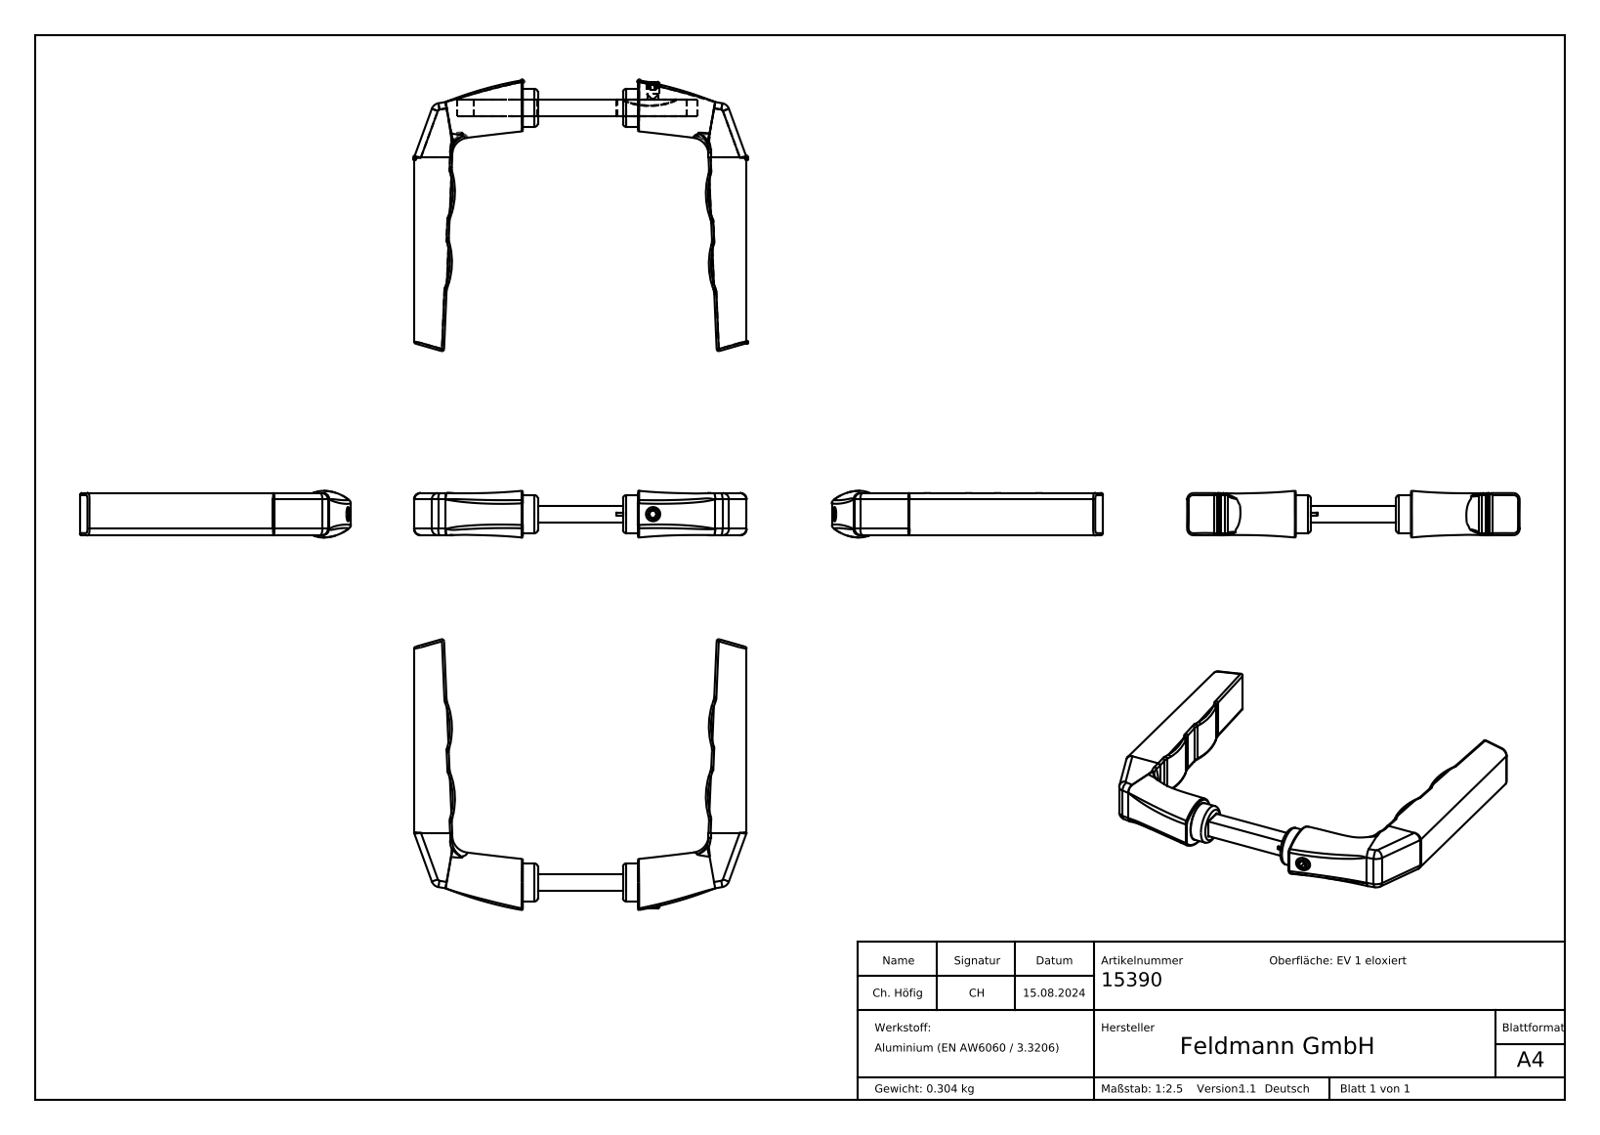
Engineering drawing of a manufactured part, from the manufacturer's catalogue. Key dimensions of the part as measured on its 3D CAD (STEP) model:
Part name (STEP PRODUCT): DIN914_DIN 914 M6x8; 15390; 15390 Teil1_15390 Teil1; 15390 Teil2_15390 Teil2
STEP written by: SolidWorks 2018 (CONFIG_CONTROL_DESIGN)
Units: millimetres
Bodies: 4 solids, 275 faces (59 planar, 60 cylindrical, 156 other)
Overall size (bounding box): 156 × 127.05 × 26.05
Volume: 99 762 mm³ · Surface area: 28 369 mm²
Round holes (diameter × count): ⌀5 ×1
Round bosses / shafts (diameter × count): ⌀17.8 ×1, ⌀6 ×1
Partial cylindrical surfaces — rounded edges, fillets, slot ends (radius × count): R0.1 ×12, R0.15 ×10, R3 ×8, R10 ×8, R1 ×6, R34.12 ×4, R4 ×2
Main face-to-face distances: 8.05, 8, 8.1, 5.85, 5.9, 13.9, 13.95, 19.8, 4.65, 4.6
